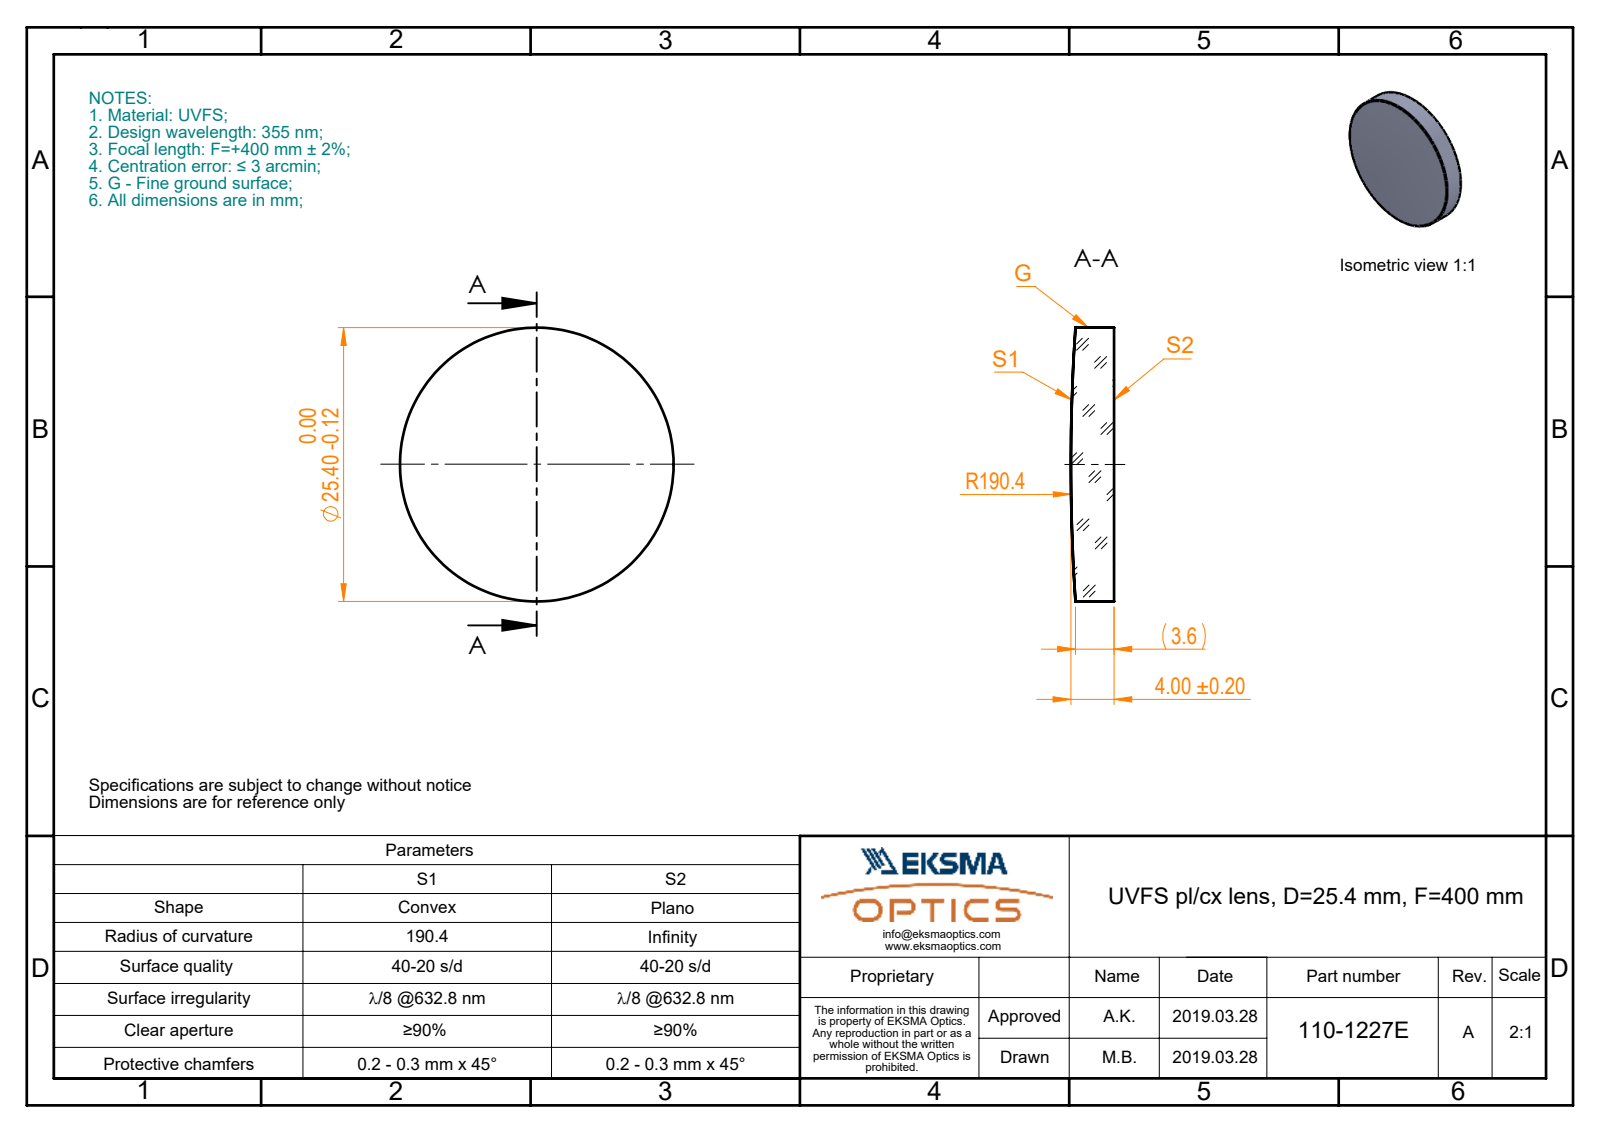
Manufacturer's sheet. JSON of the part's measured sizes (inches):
{"part_name": "110-1227E UVFS pl-cx 25.4 F400", "step_written_by": "SolidWorks 2017 (CONFIG_CONTROL_DESIGN)", "units": "inches", "bodies": {"solids": 1, "faces": 5, "planar": 1, "cylindrical": 2, "other": 2}, "overall_size": [1, 1, 0.157], "volume_in3": 0.117, "surface_area_in2": 2.013, "round_bosses_or_shafts": [[1, 1]]}
